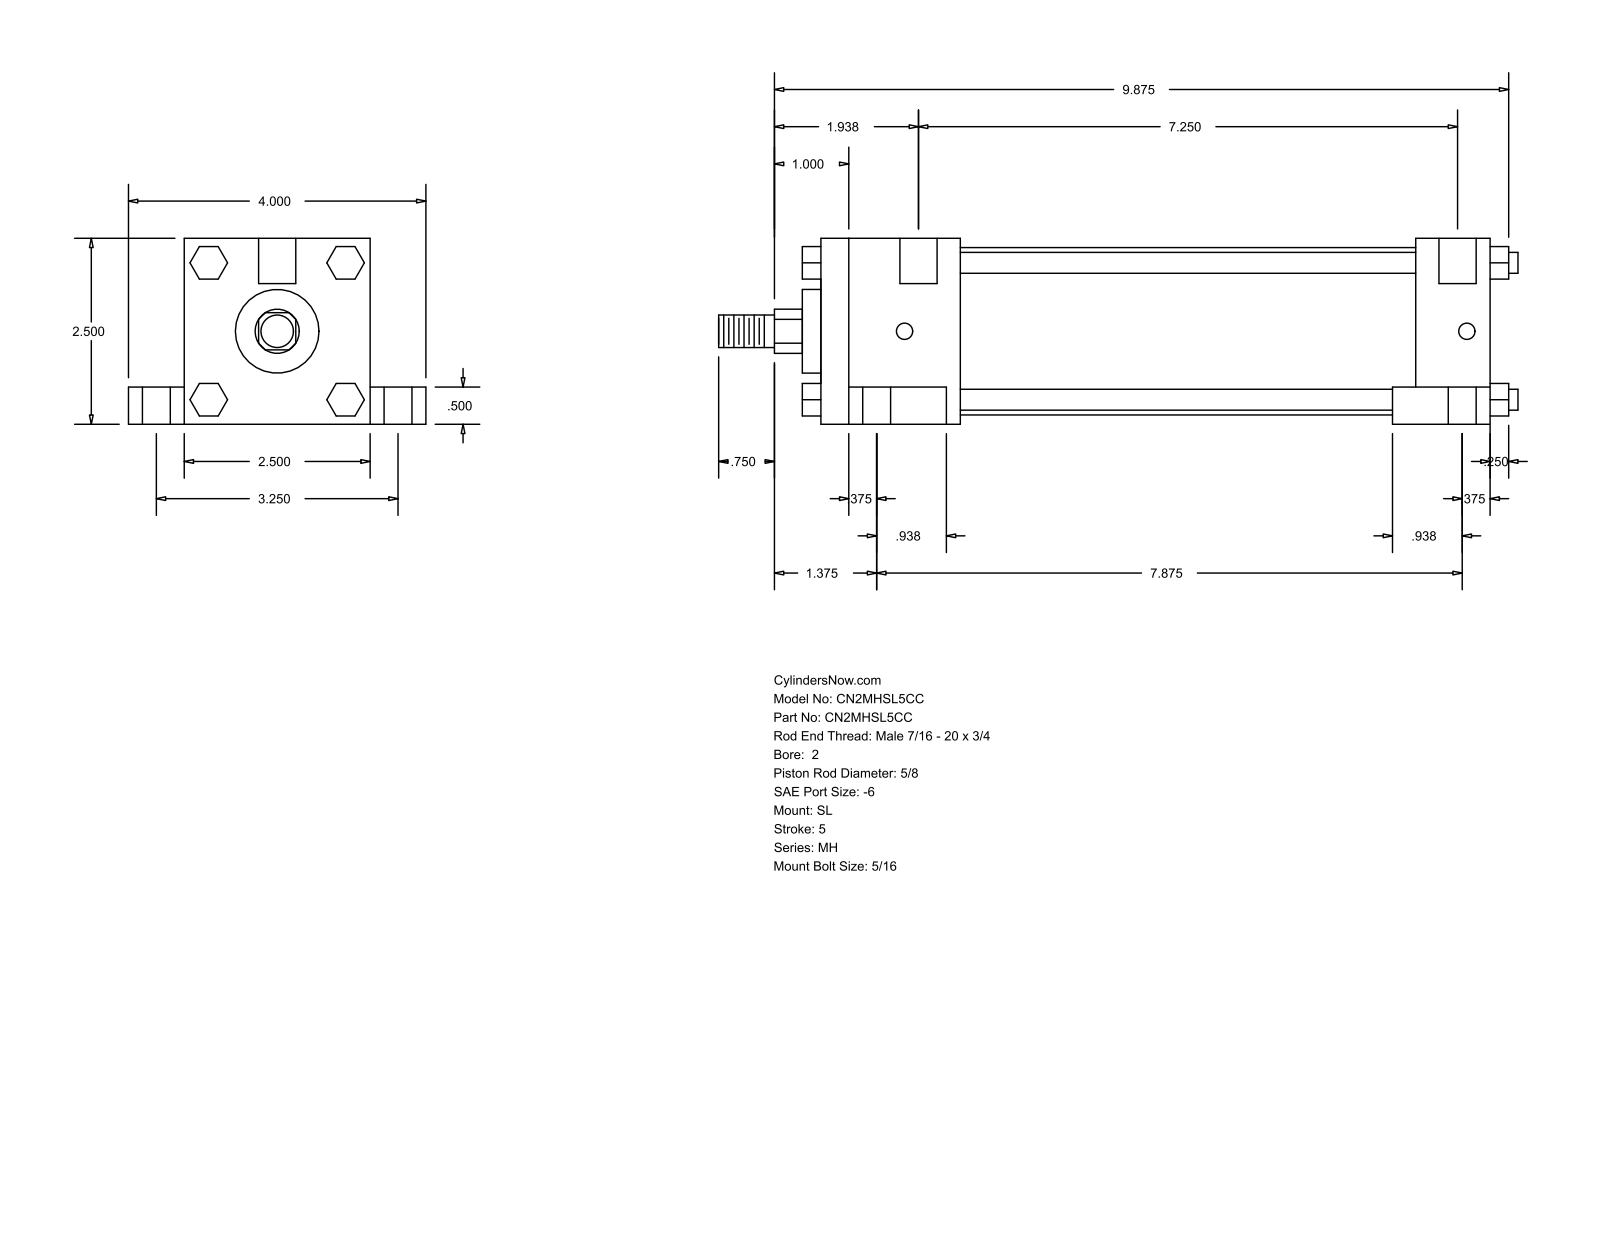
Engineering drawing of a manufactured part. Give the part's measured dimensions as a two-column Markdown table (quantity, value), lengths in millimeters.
| quantity | value |
| --- | --- |
| part name | MH_SL__0200_0.625 |
| STEP written by | GSSL Pune (CONFIG_CONTROL_DESIGN) |
| units | millimeters |
| bodies | 0 solids, 148 faces (112 planar, 36 cylindrical, 0 other) |
| overall size | 273.05 × 101.6 × 63.5 |
| round holes (diameter × count) | 5.56 × 4, 9.53 × 4, 15.88 × 4, 12.7 × 2 |
| round bosses / shafts (diameter × count) | 7.14 × 4, 57.15 × 1, 28.57 × 1, 15.88 × 1, 11.11 × 1 |
| partial cylindrical surfaces (radius × count) | 7.54 × 1 |
| main face-to-face distances | 63.5, 228.59, 12.7, 19.05, 82.55, 50.8, 25.4, 203.19, 47.62, 155.57 |
| hole center spacings | 41.3, 42.36, 43.67, 82.54, 190.27, 192.09, 194.92, 200.03 |
